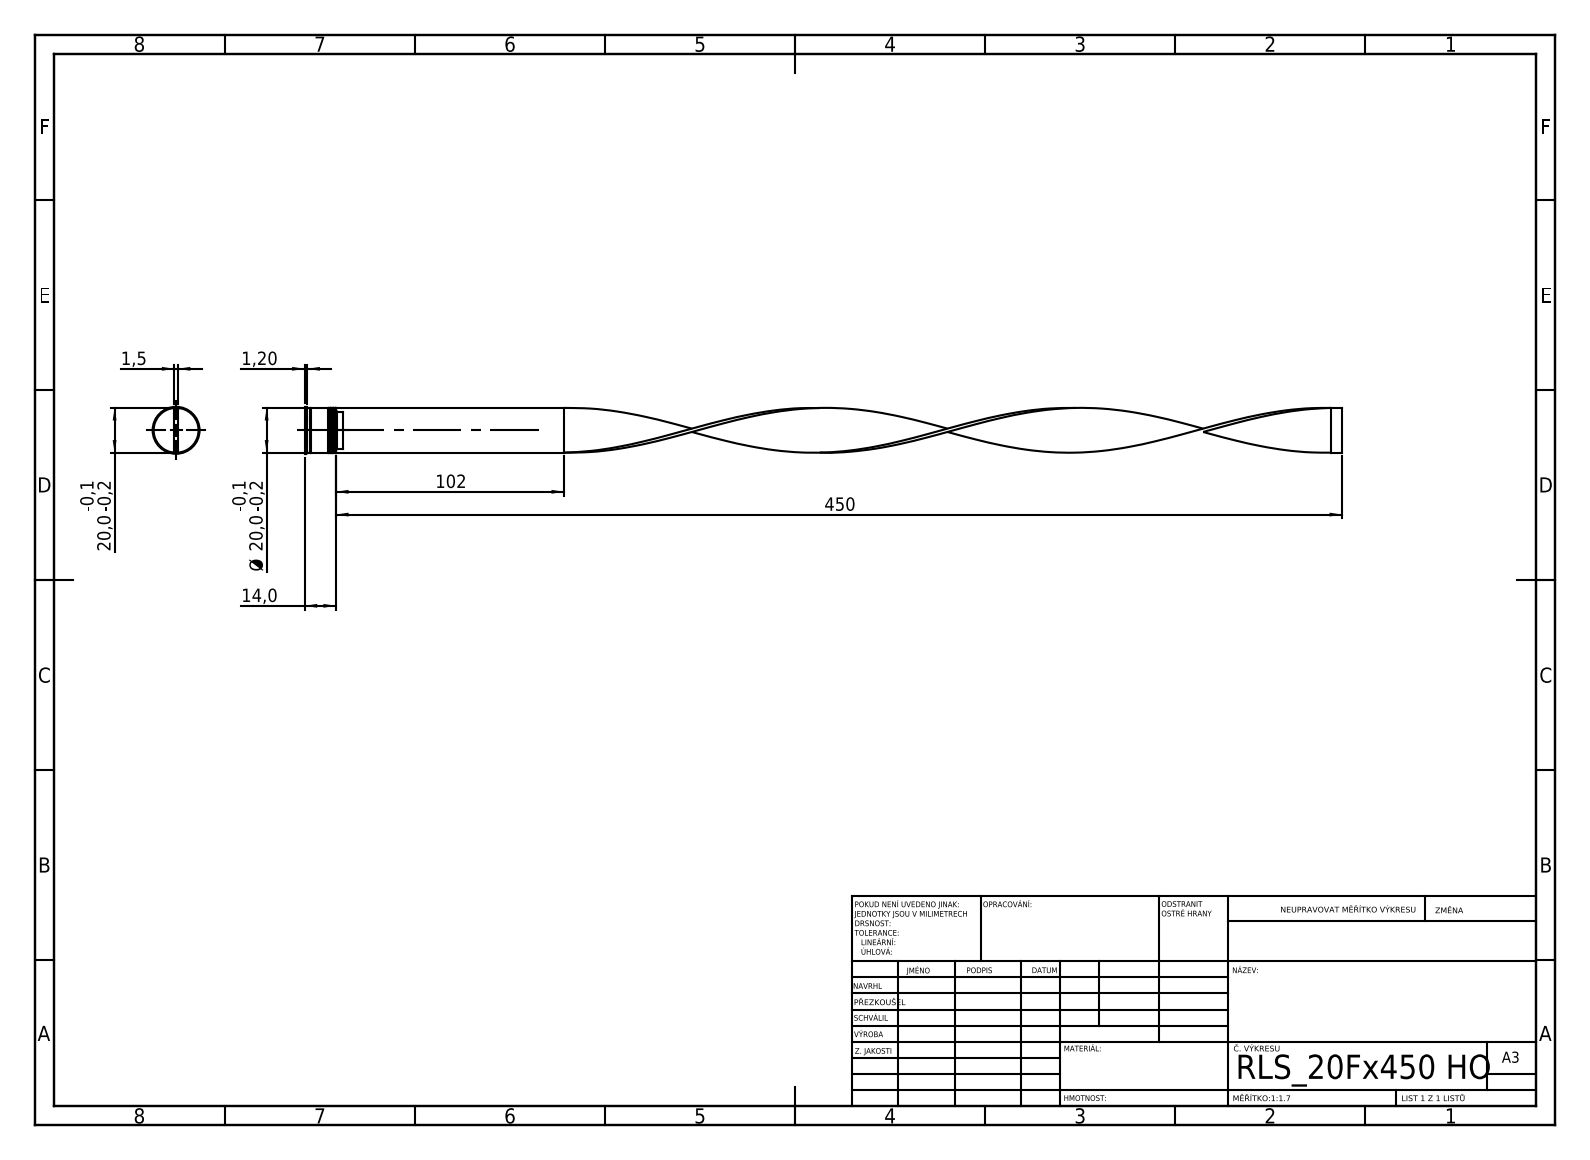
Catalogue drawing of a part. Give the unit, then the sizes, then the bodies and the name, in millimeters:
Units: millimetres
Overall size (bounding box): 464 × 21 × 21
Round bosses / shafts (diameter × count): ⌀21 ×1, ⌀20 ×1, ⌀19.4 ×1, ⌀16.8 ×1
Partial cylindrical surfaces — rounded edges, fillets, slot ends (radius × count): R8.5 ×1
Main face-to-face distances: 1.5, 0.7, 2.2, 0.8, 11.7, 11, 10.2, 9.5, 16, 4.3
Volume: 18 650 mm³ · Surface area: 22 621 mm²
Bodies: 3 solids, 98 faces (43 planar, 28 cylindrical, 27 other)
STEP written by: SolidWorks 2019 (CONFIG_CONTROL_DESIGN)
